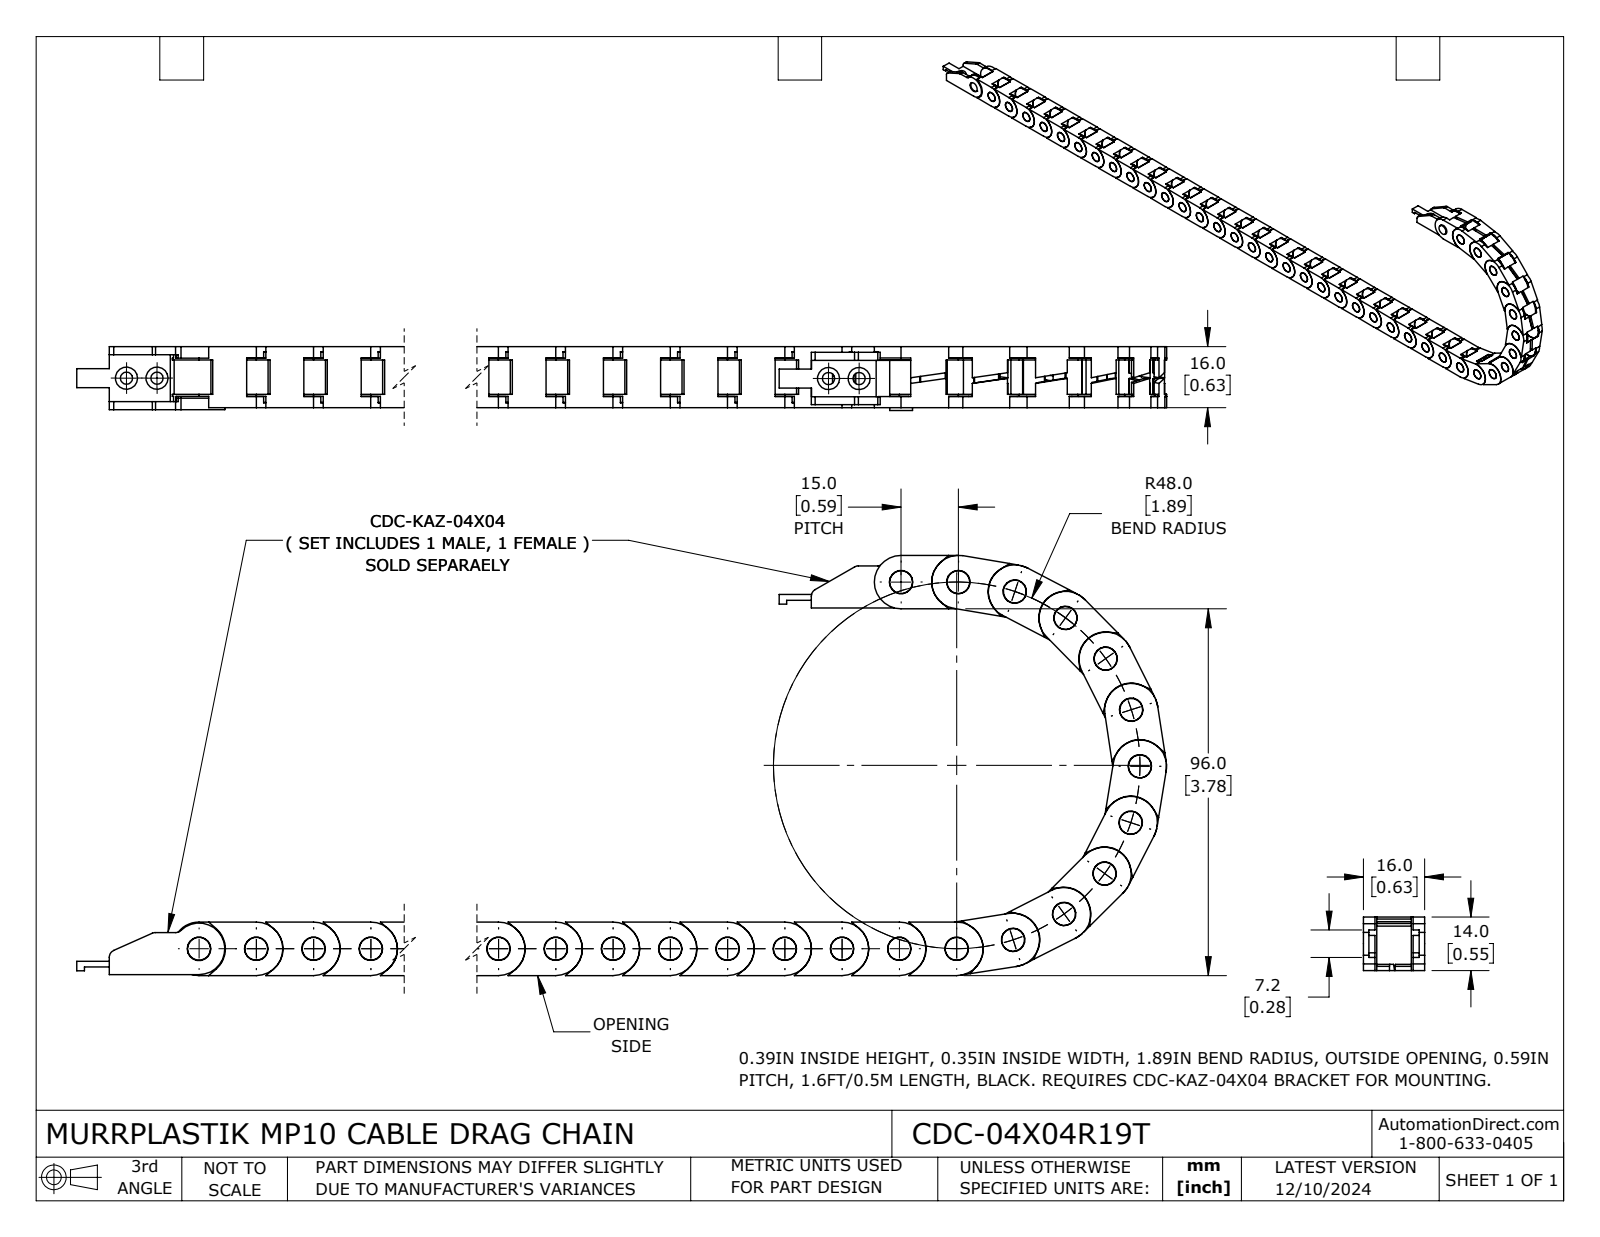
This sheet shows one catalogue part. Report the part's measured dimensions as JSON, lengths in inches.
{"part_name": "CDC-04X04R19T", "step_written_by": "SolidWorks 2024 (AUTOMOTIVE_DESIGN)", "units": "inches", "bodies": {"solids": 40, "faces": 2718, "planar": 1842, "cylindrical": 872, "other": 4}, "overall_size": [19.961, 4.331, 0.657], "volume_in3": 3.956, "surface_area_in2": 142.9, "round_holes": [[0.242, 38], [0.126, 4], [0.244, 1]], "round_bosses_or_shafts": [[0.236, 39], [0.551, 28]], "partial_cylinders_radius": [[0.02, 190], [0.274, 48], [0.142, 38], [0.457, 38], [0.276, 20], [0.079, 6], [0.039, 2], [0.266, 2]], "face_to_face_distances": [0.138, 0.492, 0.354, 0.63, 0.087, 0.051, 0.063, 0.02, 0.461, 0.512], "hole_center_spacings": [0.591, 1.181, 1.772, 2.362, 2.953, 3.543, 4.134, 4.724]}
